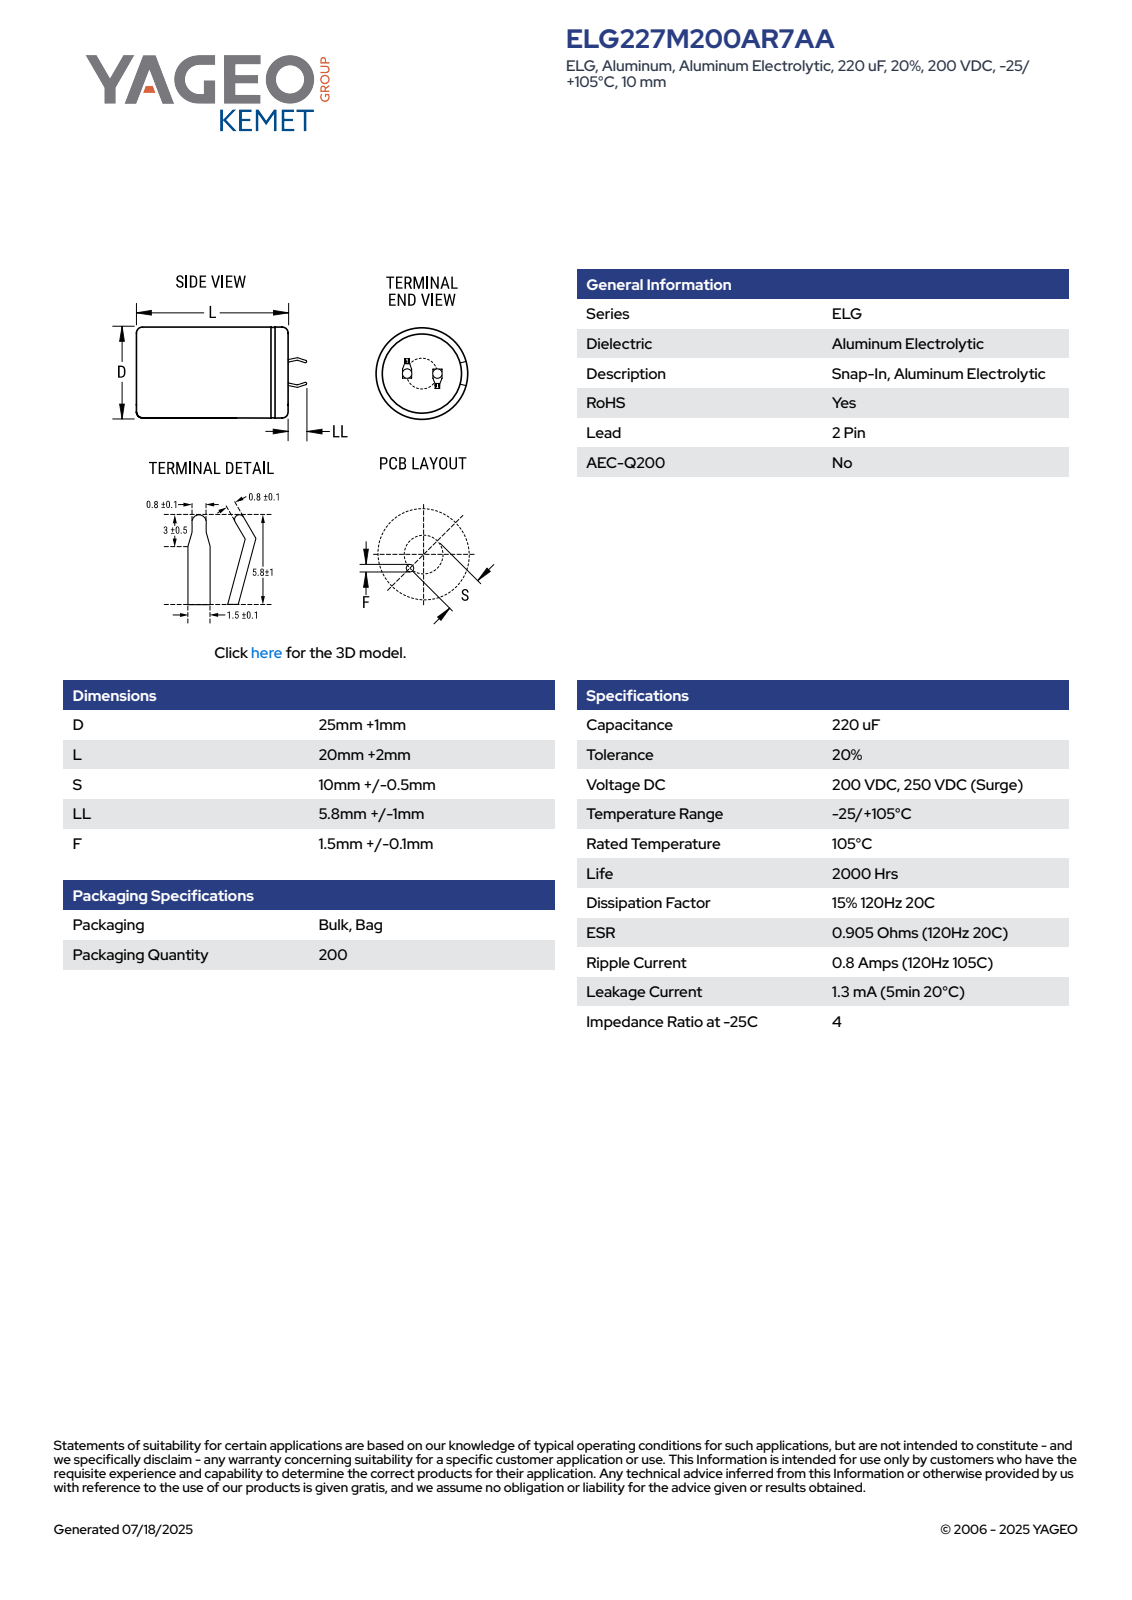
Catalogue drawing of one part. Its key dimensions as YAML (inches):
part_name: "CARS_K2P_25X20_D26L22S10LL6.8F1.6"
step_written_by: "SolidWorks 2014 (AUTOMOTIVE_DESIGN)"
units: inches
bodies: {solids: 1, faces: 100, planar: 52, cylindrical: 9, other: 39}
overall_size: [1.133, 1.024, 1.024]
volume: 0.701
surface_area: 4.461
round_holes:
  - {diameter: 0.906, count: 1}
round_bosses_or_shafts:
  - {diameter: 1.024, count: 1}
partial_cylinders:
  - {radius: 0.511, count: 1}
face_to_face_distances: [0.866, 0.024, 0.885, 0.02, 0.279, 0.3, 0.03, 0.053, 0.302, 0.255]
